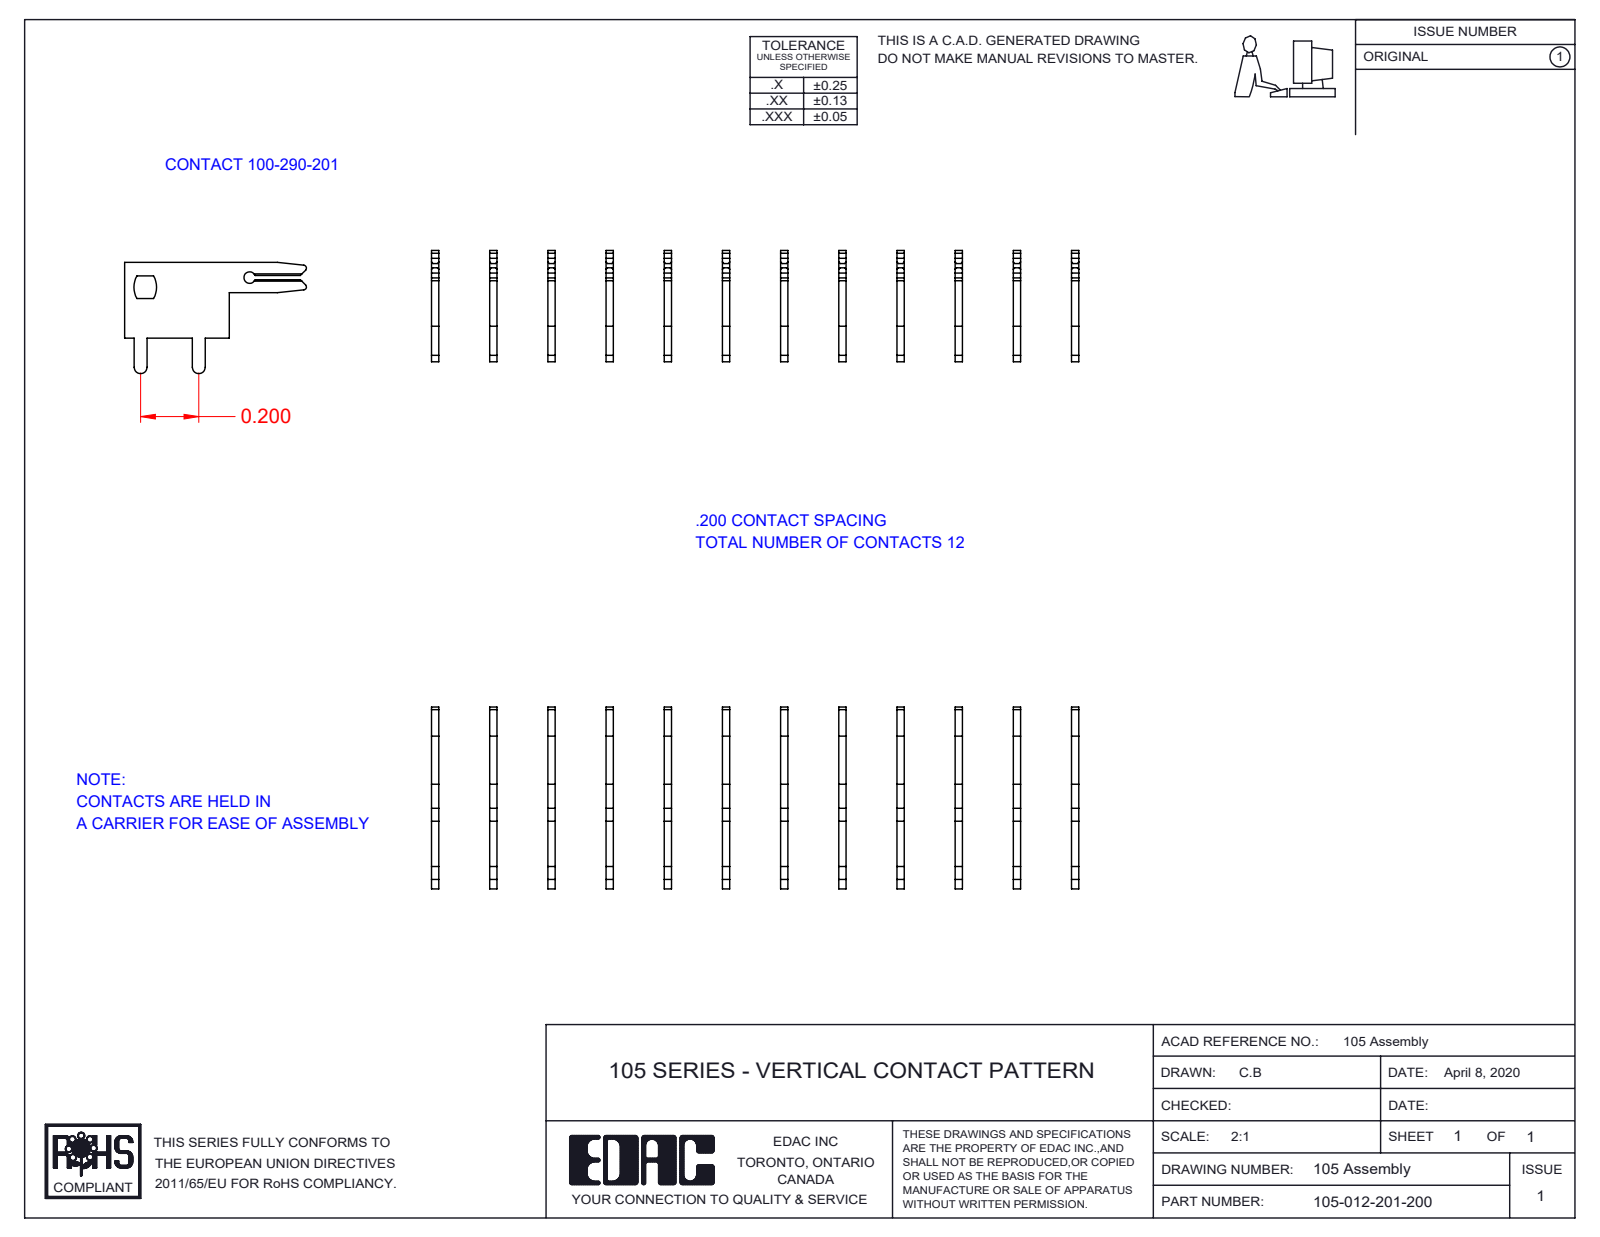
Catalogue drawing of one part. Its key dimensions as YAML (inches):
part_name: "105-012-201-200; 100-290-001_100-290-201"
step_written_by: "SolidWorks 2016 (CONFIG_CONTROL_DESIGN)"
units: inches
bodies: {solids: 12, faces: 420, planar: 300, cylindrical: 120, other: 0}
overall_size: [2.225, 0.625, 0.382]
volume: 0.036
surface_area: 3.738
round_holes:
  - {diameter: 0.04, count: 1}
partial_cylinders:
  - {radius: 0.01, count: 2}
  - {radius: 0.022, count: 2}
  - {radius: 0.078, count: 2}
face_to_face_distances: [0.2, 0.4, 0.6, 0.8, 1, 0.025, 0.225, 0.425, 0.625, 0.825]
